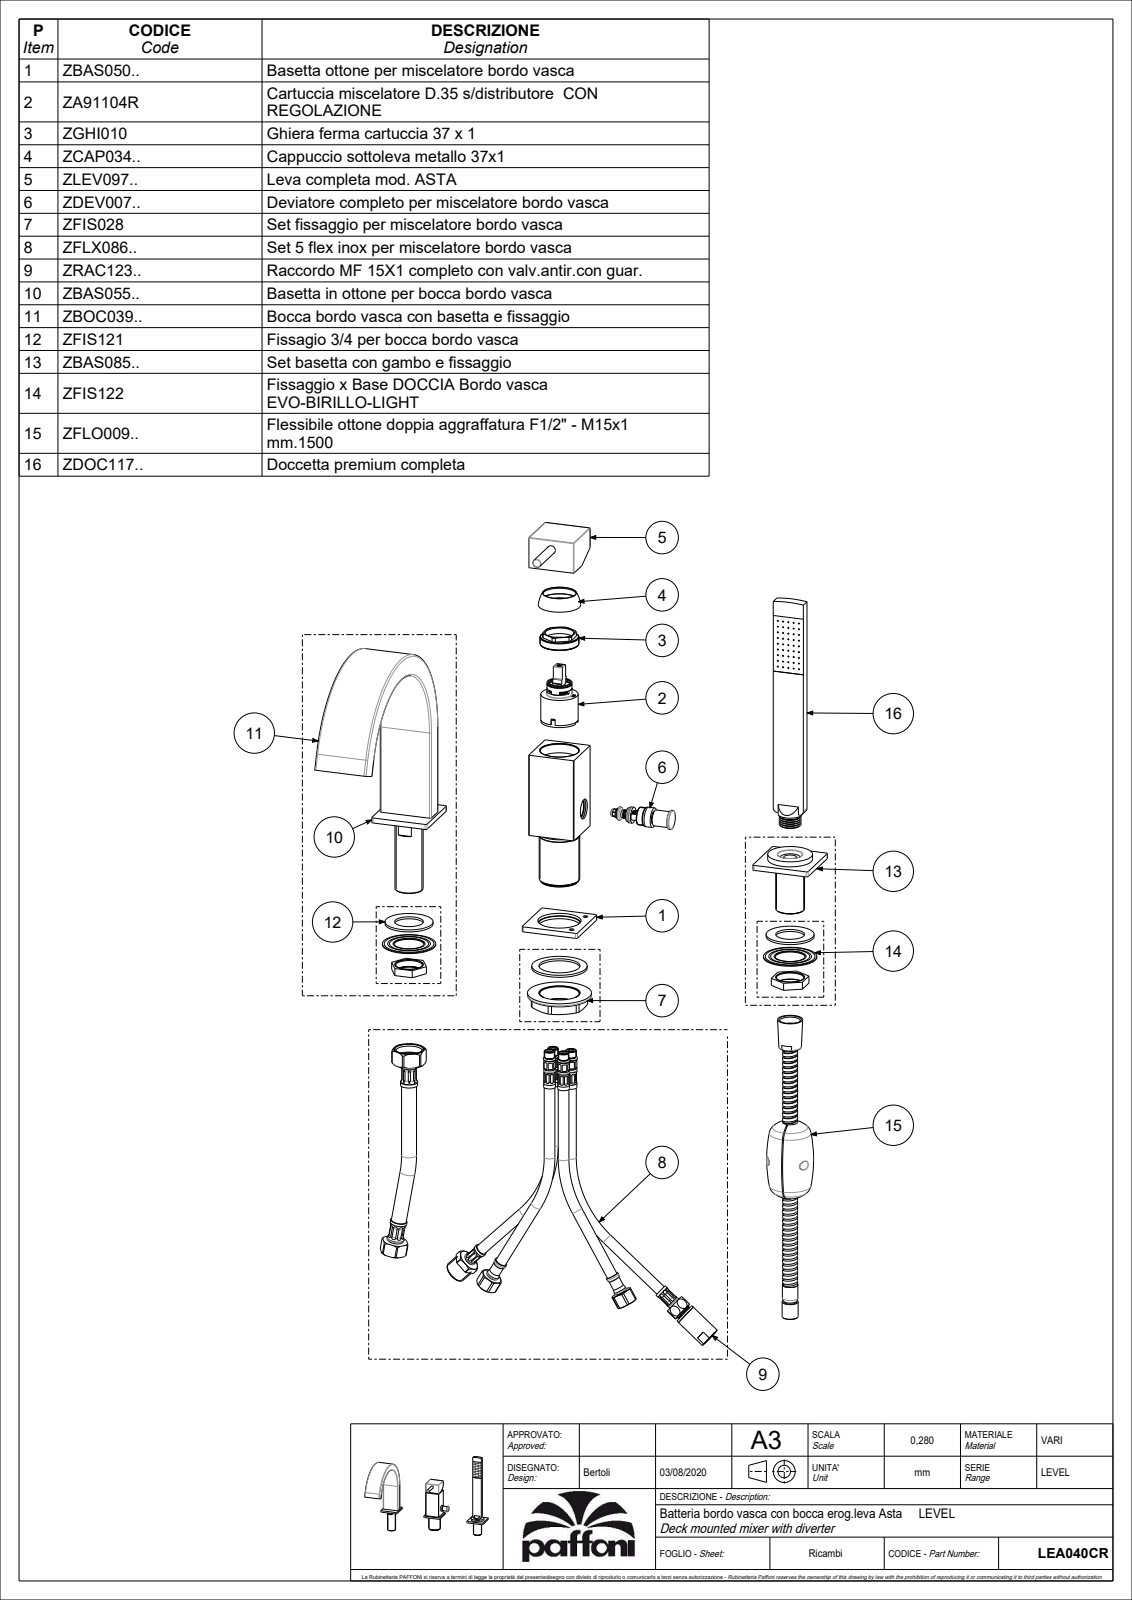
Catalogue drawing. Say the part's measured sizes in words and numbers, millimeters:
The part is named "LEA040CR". Its 3-D file was written by "CREO PARAMETRIC BY PTC INC, 2020044 (CONFIG_CONTROL_DESIGN)". It is 7 solids with 1566 faces: 965 planar, 385 cylindrical and 216 other. Overall it measures 355 by 223 by 216.96 millimeters. Its volume is 433 140 cubic millimeters and its surface area 199 772 square millimeters. Round holes: 7 of diameter 7, 3 of diameter 48, 2 of diameter 4, 2 of diameter 4.5, 1 of diameter 3.1, 1 of diameter 3.3, 1 of diameter 3.4, 1 of diameter 4.3, 1 of diameter 5, 1 of diameter 5.5, 1 of diameter 7.2, 1 of diameter 8.1. Round bosses or shafts: 11 of diameter 2, 3 of diameter 42.5, 2 of diameter 15, 1 of diameter 42, 1 of diameter 40, 1 of diameter 38, 1 of diameter 35, 1 of diameter 34.8. Partial cylindrical surfaces (rounded edges, fillets, slot ends): 37 of radius 0.5, 24 of radius 1.5, 11 of radius 0.15, 4 of radius 0.3, 2 of radius 1, 2 of radius 4, 1 of radius 3, 1 of radius 3.9. The main face-to-face distances are 3.5, 5, 17.5, 32.5, 27.5, 12.5, 15, 47.5, 45, 1.5. The hole center spacings are 3, 8.6, 10.63, 14, 14.32, 143.09, 143.22, 150.
